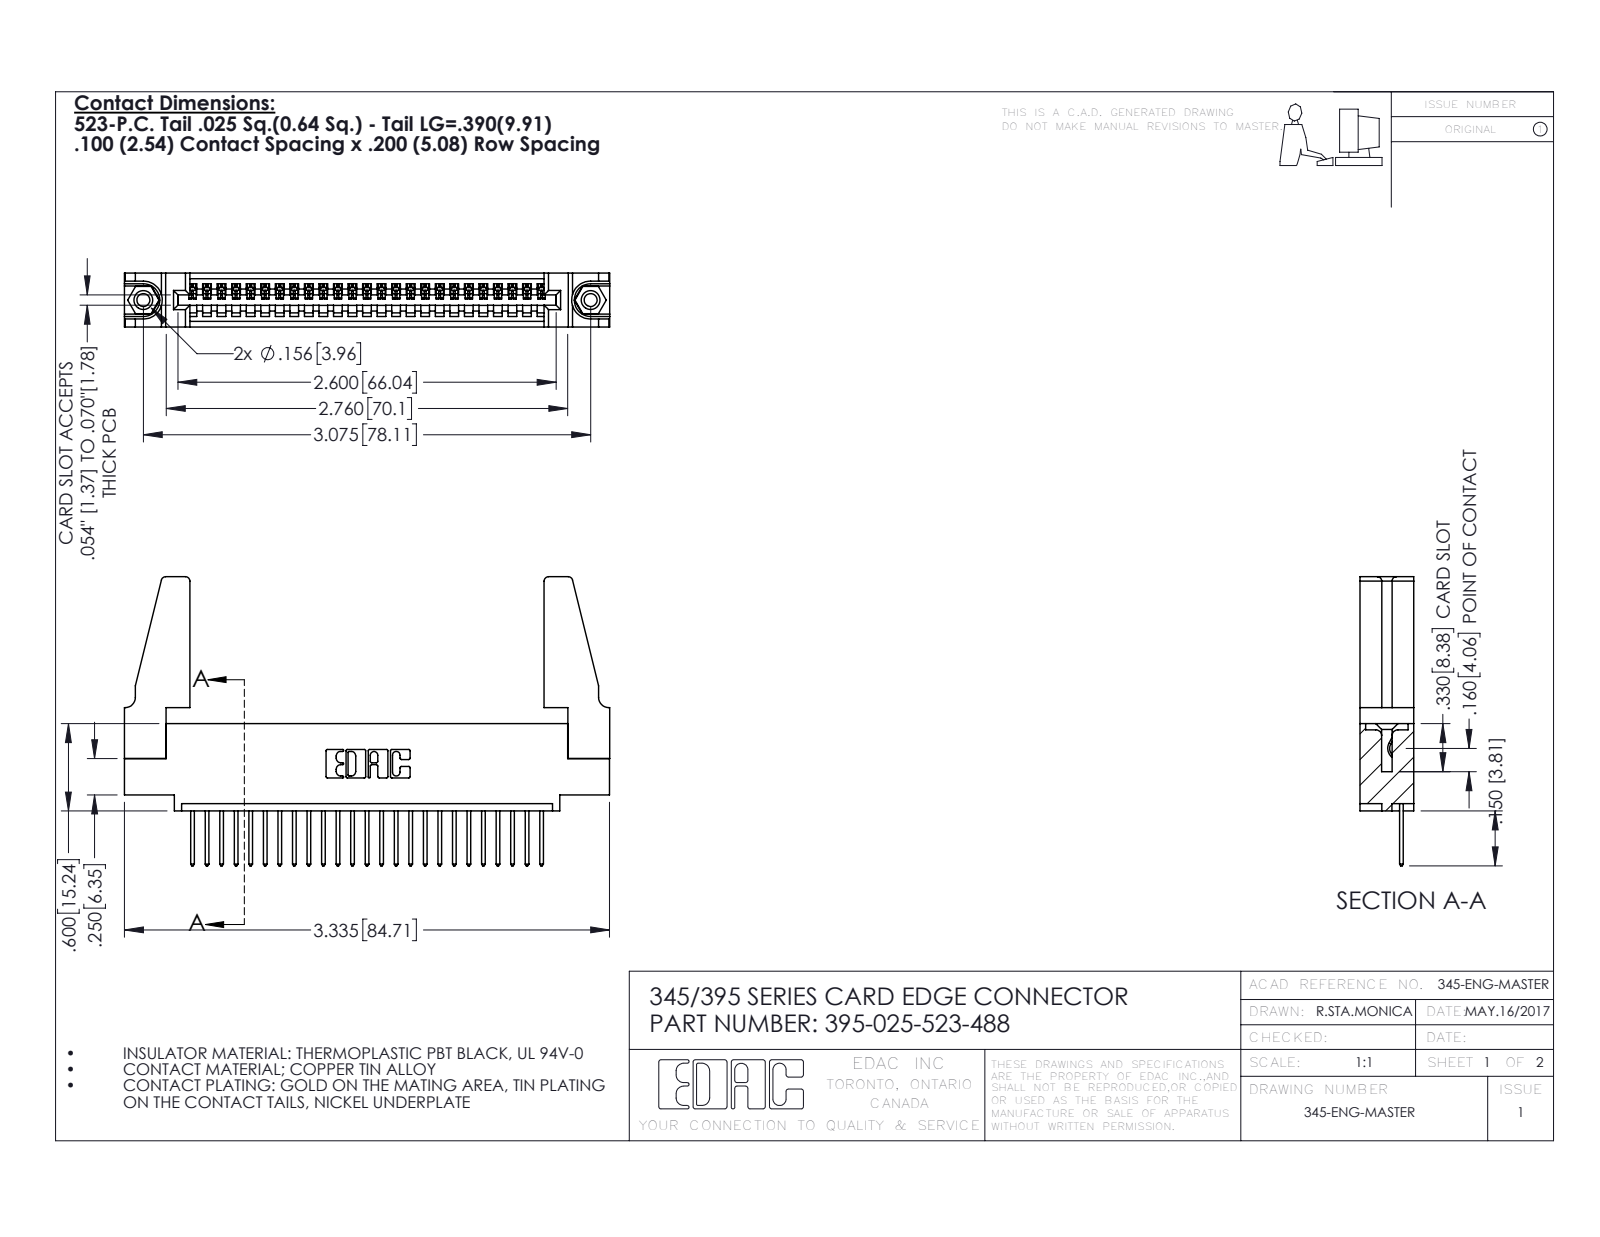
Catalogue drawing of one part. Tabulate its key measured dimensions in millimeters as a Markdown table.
| quantity | value |
| --- | --- |
| part name | 345-292-001_345-293-123; 395-025-523-488; 345-220-078_345-220-088; 345-250-001_345-250-001-102 (+1 more) |
| STEP written by | SolidWorks 2016 (CONFIG_CONTROL_DESIGN) |
| units | millimeters |
| bodies | 30 solids, 1704 faces (1156 planar, 532 cylindrical, 16 other) |
| overall size | 84.7 × 50.5 × 9.4 |
| volume | 11 100 mm³ |
| surface area | 13 410 mm² |
| round holes (diameter × count) | 2.3 × 2, 3.2 × 2, 4 × 2, 1.6 × 1 |
| round bosses / shafts (diameter × count) | 3.9 × 2 |
| partial cylindrical surfaces (radius × count) | 0.2 × 50, 0.3 × 50, 0.3 × 22, 0.8 × 8, 0.2 × 6, 0.8 × 6, 0.7 × 3, 0.8 × 2 |
| main face-to-face distances | 1.8, 9.4, 7.6, 5.1, 2.5, 6.9, 0.6, 5.7, 3.8, 1.8 |
| hole center spacings | 6.9, 72.1, 78.1 |
